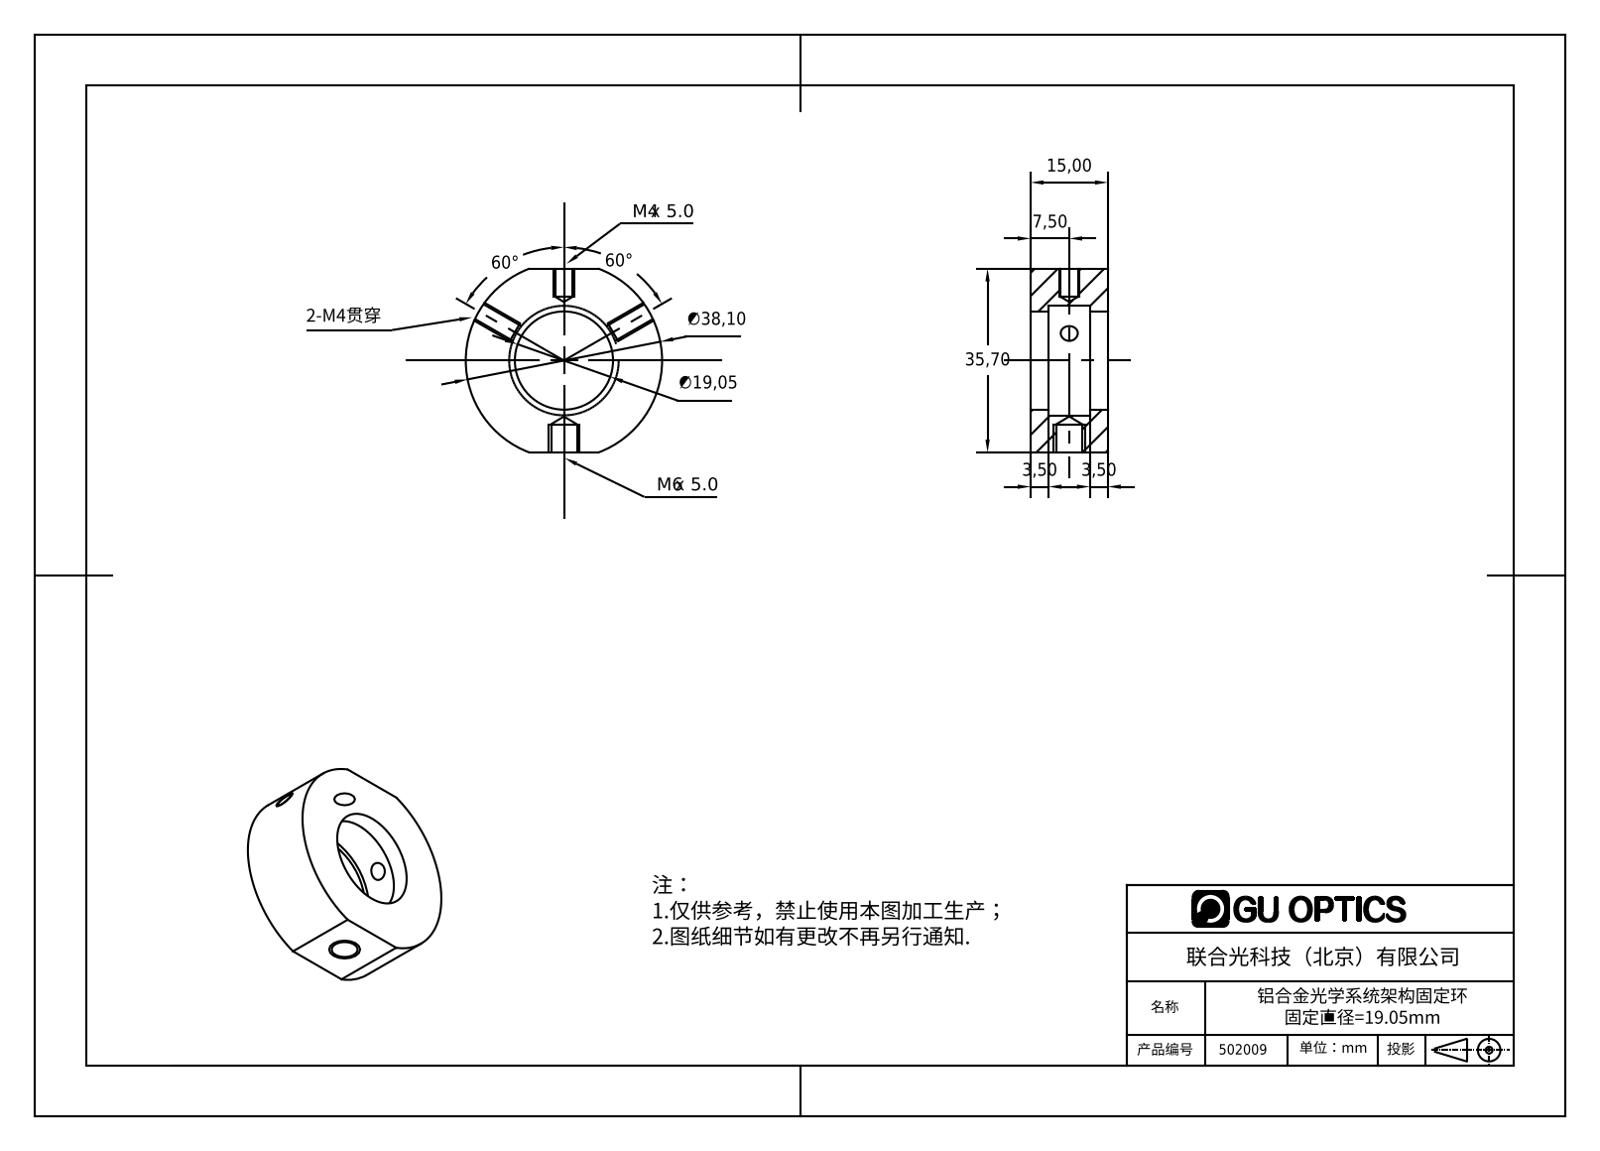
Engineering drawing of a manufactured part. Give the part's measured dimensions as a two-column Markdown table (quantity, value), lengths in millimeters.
| quantity | value |
| --- | --- |
| part name | 502009 |
| STEP written by | SolidWorks 2016 (CONFIG_CONTROL_DESIGN) |
| units | millimeters |
| bodies | 1 solid, 27 faces (6 planar, 17 cylindrical, 4 other) |
| overall size | 38.1 × 35.7 × 15 |
| volume | 11 635 mm³ |
| surface area | 4 835 mm² |
| round holes (diameter × count) | 3.3 × 3, 5 × 1, 19.05 × 1, 21.25 × 1 |
| partial cylindrical surfaces (radius × count) | 19.05 × 1 |
| main face-to-face distances | 15, 35.7, 3.5, 11.5, 8 |
